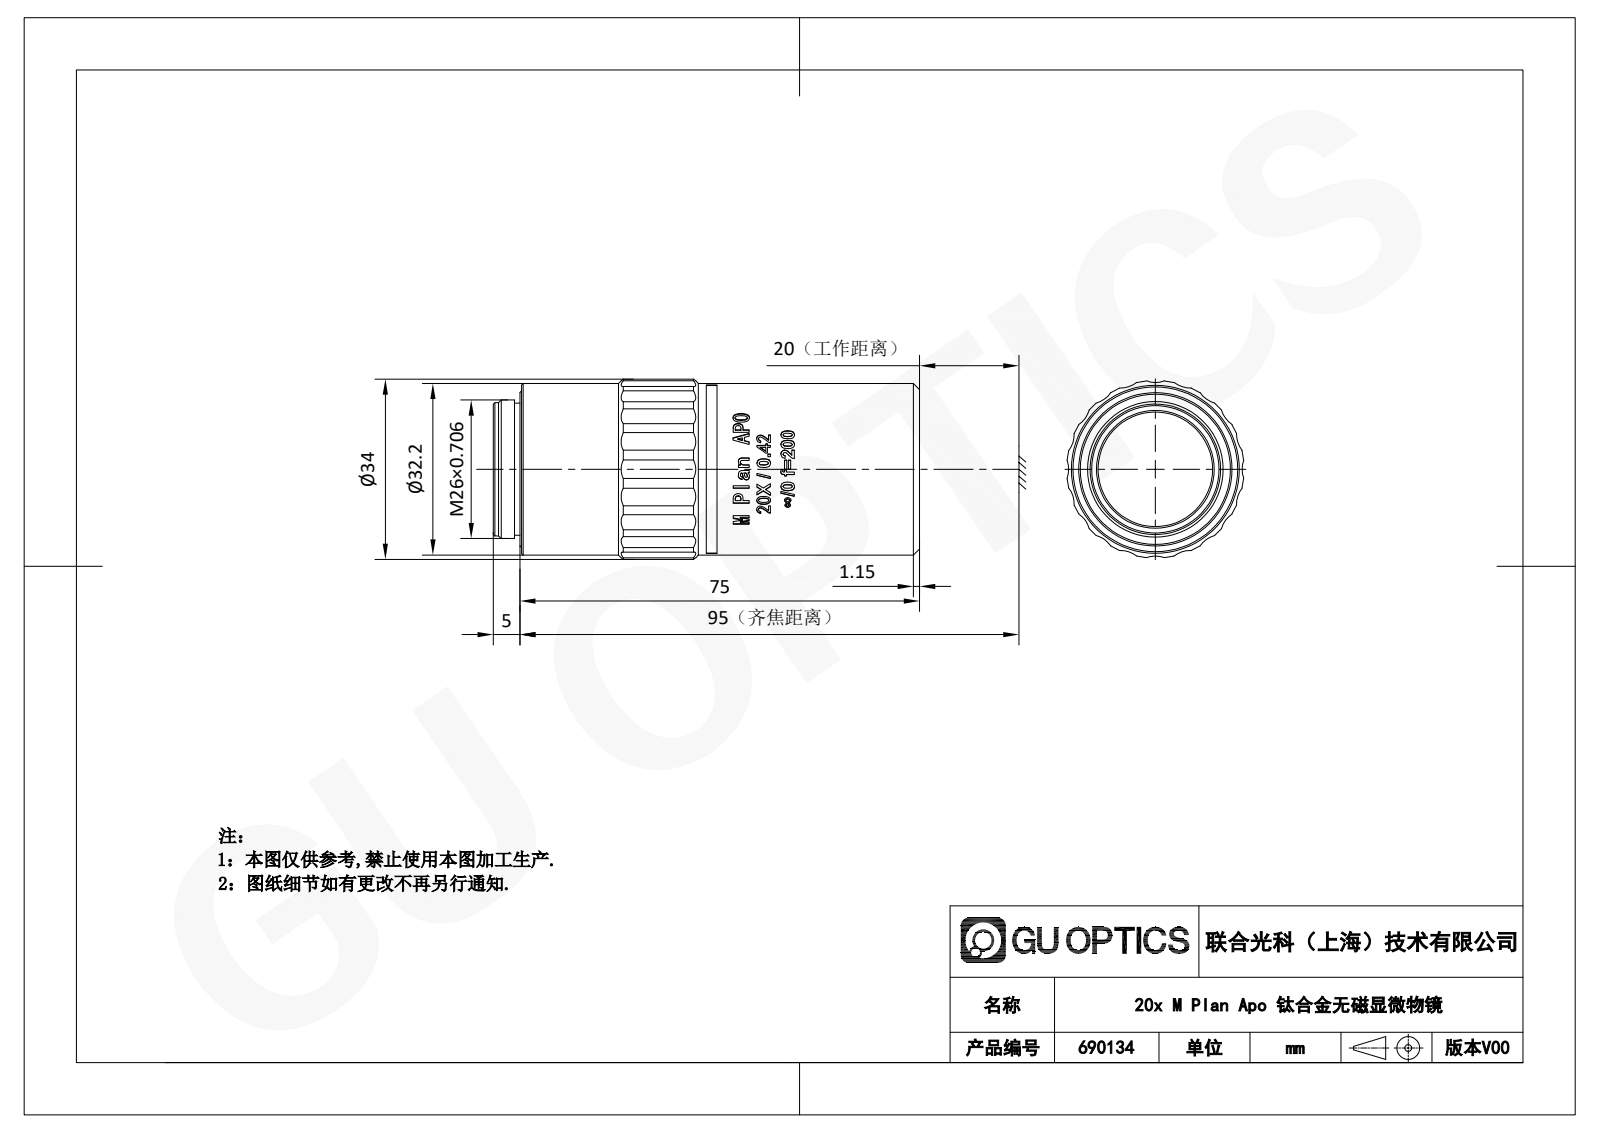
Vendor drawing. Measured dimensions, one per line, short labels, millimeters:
name: 690134
written by: SolidWorks 2020 (CONFIG_CONTROL_DESIGN)
unit: mm
bodies: 1 solid, 364 faces (114 planar, 87 cylindrical, 163 other)
size: 80 × 33.82 × 33.82
volume: 62 435 mm³; area: 10 140 mm²
holes: 1× ⌀22, 1× ⌀24
bosses: 1× ⌀32.2, 1× ⌀32, 1× ⌀26, 1× ⌀25, 1× ⌀24.8
rounds: 20× R5, 1× R15.9, 1× R17
face distances: 1.3, 76.3, 75, 1.6, 74.7, 3.7, 5, 5.3, 80, 4
